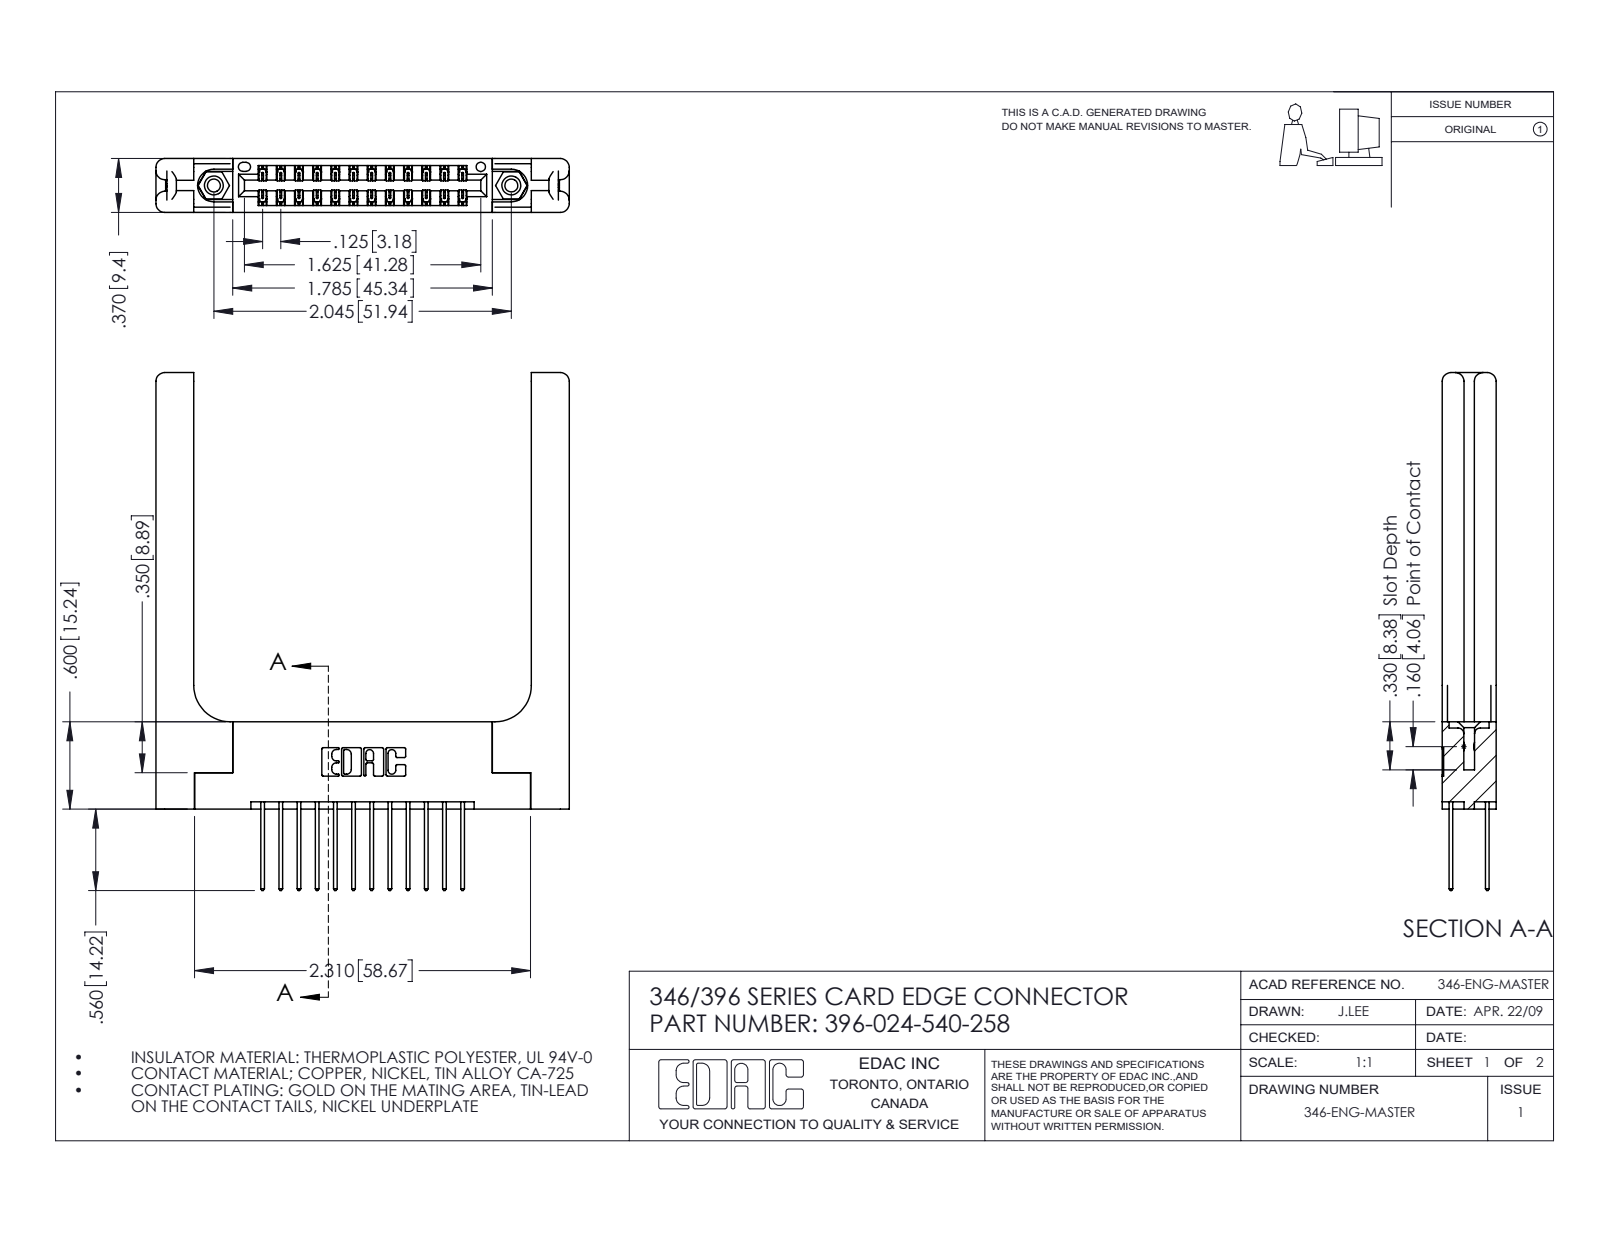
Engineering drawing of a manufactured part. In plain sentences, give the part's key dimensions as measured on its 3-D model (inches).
The part is named "345-250-001_345-250-001-102; 345-292-001_345-293-140; 346 Part_Flush Mounting Lugs - 0.156 Dia-TH; 396-024-540-258 (+1 more)". Its 3-D file was written by "SolidWorks 2016 (CONFIG_CONTROL_DESIGN)". It is 29 solids with 1626 faces: 1064 planar, 502 cylindrical and 60 other. Overall it measures 3.56 by 2.841 by 0.37 inches. Its volume is 0.878 cubic inches and its surface area 22.33 square inches. Round holes: 2 of diameter 0.089, 2 of diameter 0.125, 2 of diameter 0.156, 1 of diameter 0.064. Round bosses or shafts: 2 of diameter 0.155. Partial cylindrical surfaces (rounded edges, fillets, slot ends): 36 of radius 0.006, 24 of radius 0.01, 22 of radius 0.01, 16 of radius 0.06, 6 of radius 0.007, 6 of radius 0.031, 3 of radius 0.026, 2 of radius 0.014. The main face-to-face distances are 0.37, 0.072, 0.15, 0.148, 0.048, 0.322, 0.25, 0.077, 0.102, 0.22. The hole center spacings are 0.246, 1.839, 2.045.
